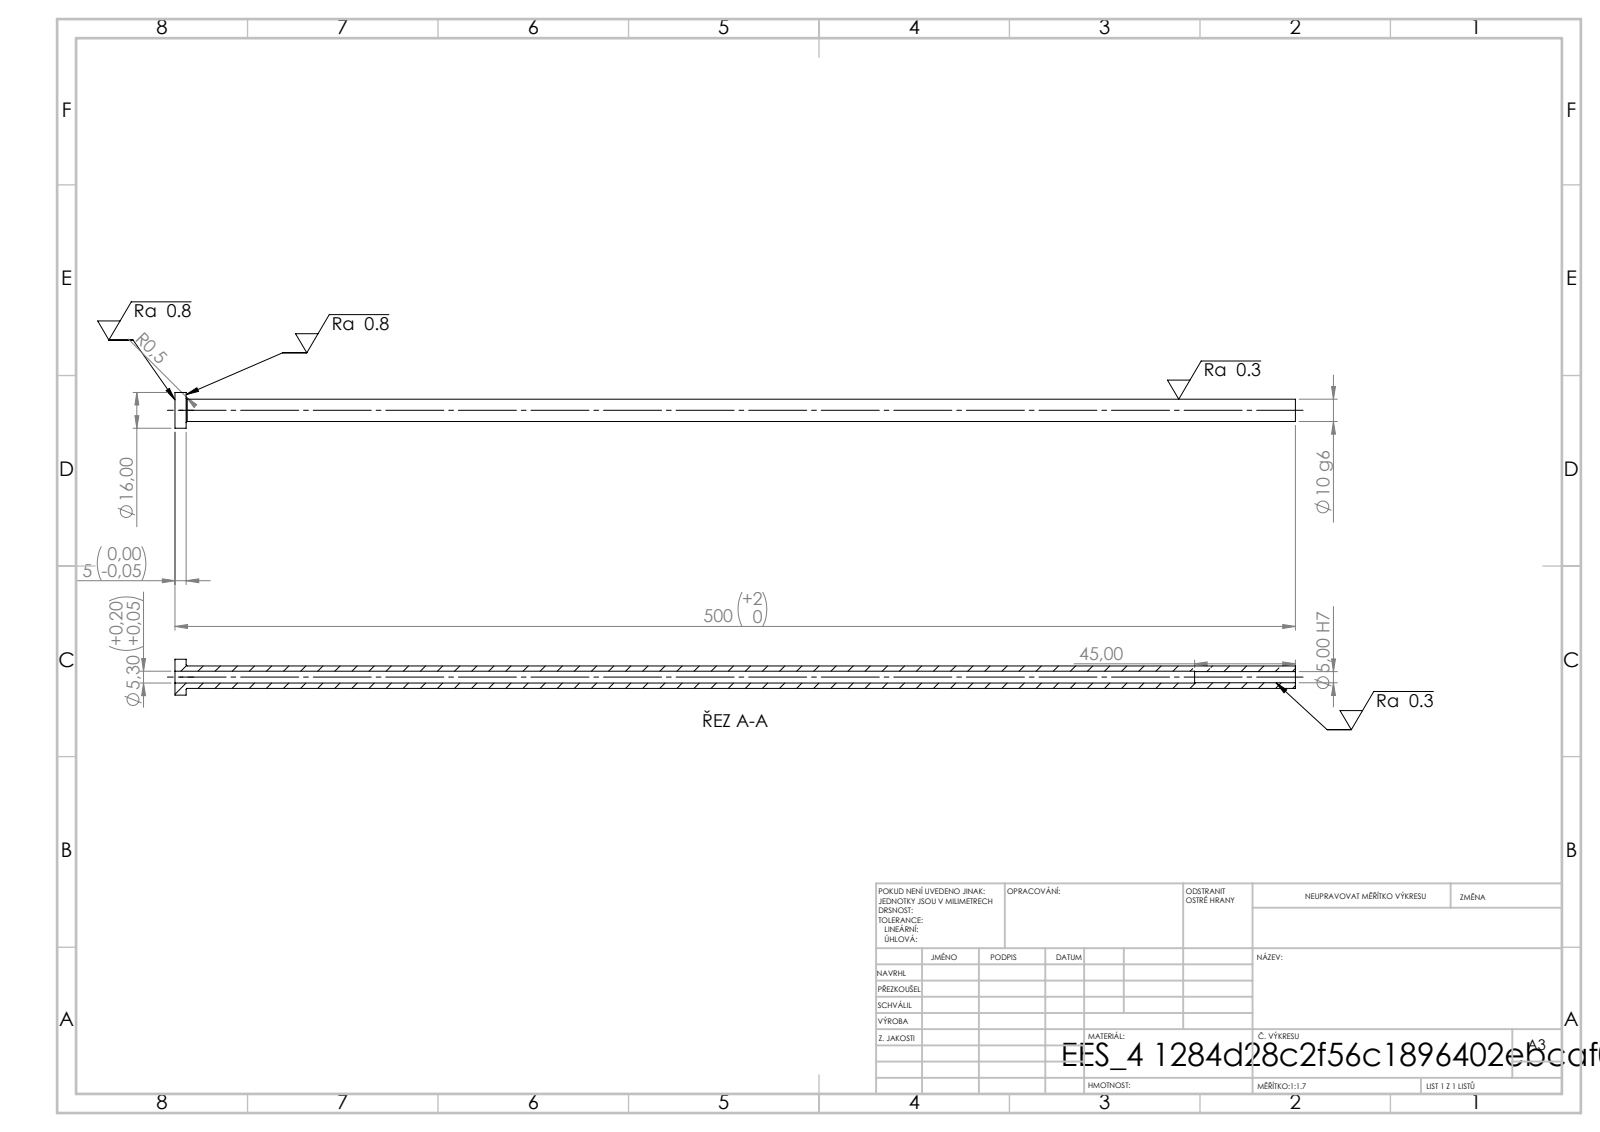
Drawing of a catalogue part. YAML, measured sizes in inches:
step_written_by: "SolidWorks 2019 (CONFIG_CONTROL_DESIGN)"
units: inches
bodies: {solids: 1, faces: 14, planar: 4, cylindrical: 8, other: 2}
overall_size: [19.685, 0.63, 0.63]
volume: 1.767
surface_area: 37.88
round_holes:
  - {diameter: 0.197, count: 1}
  - {diameter: 0.209, count: 1}
round_bosses_or_shafts:
  - {diameter: 0.63, count: 1}
  - {diameter: 0.394, count: 1}
face_to_face_distances: [0.197, 19.685, 19.488, 17.913, 17.717, 1.772]
